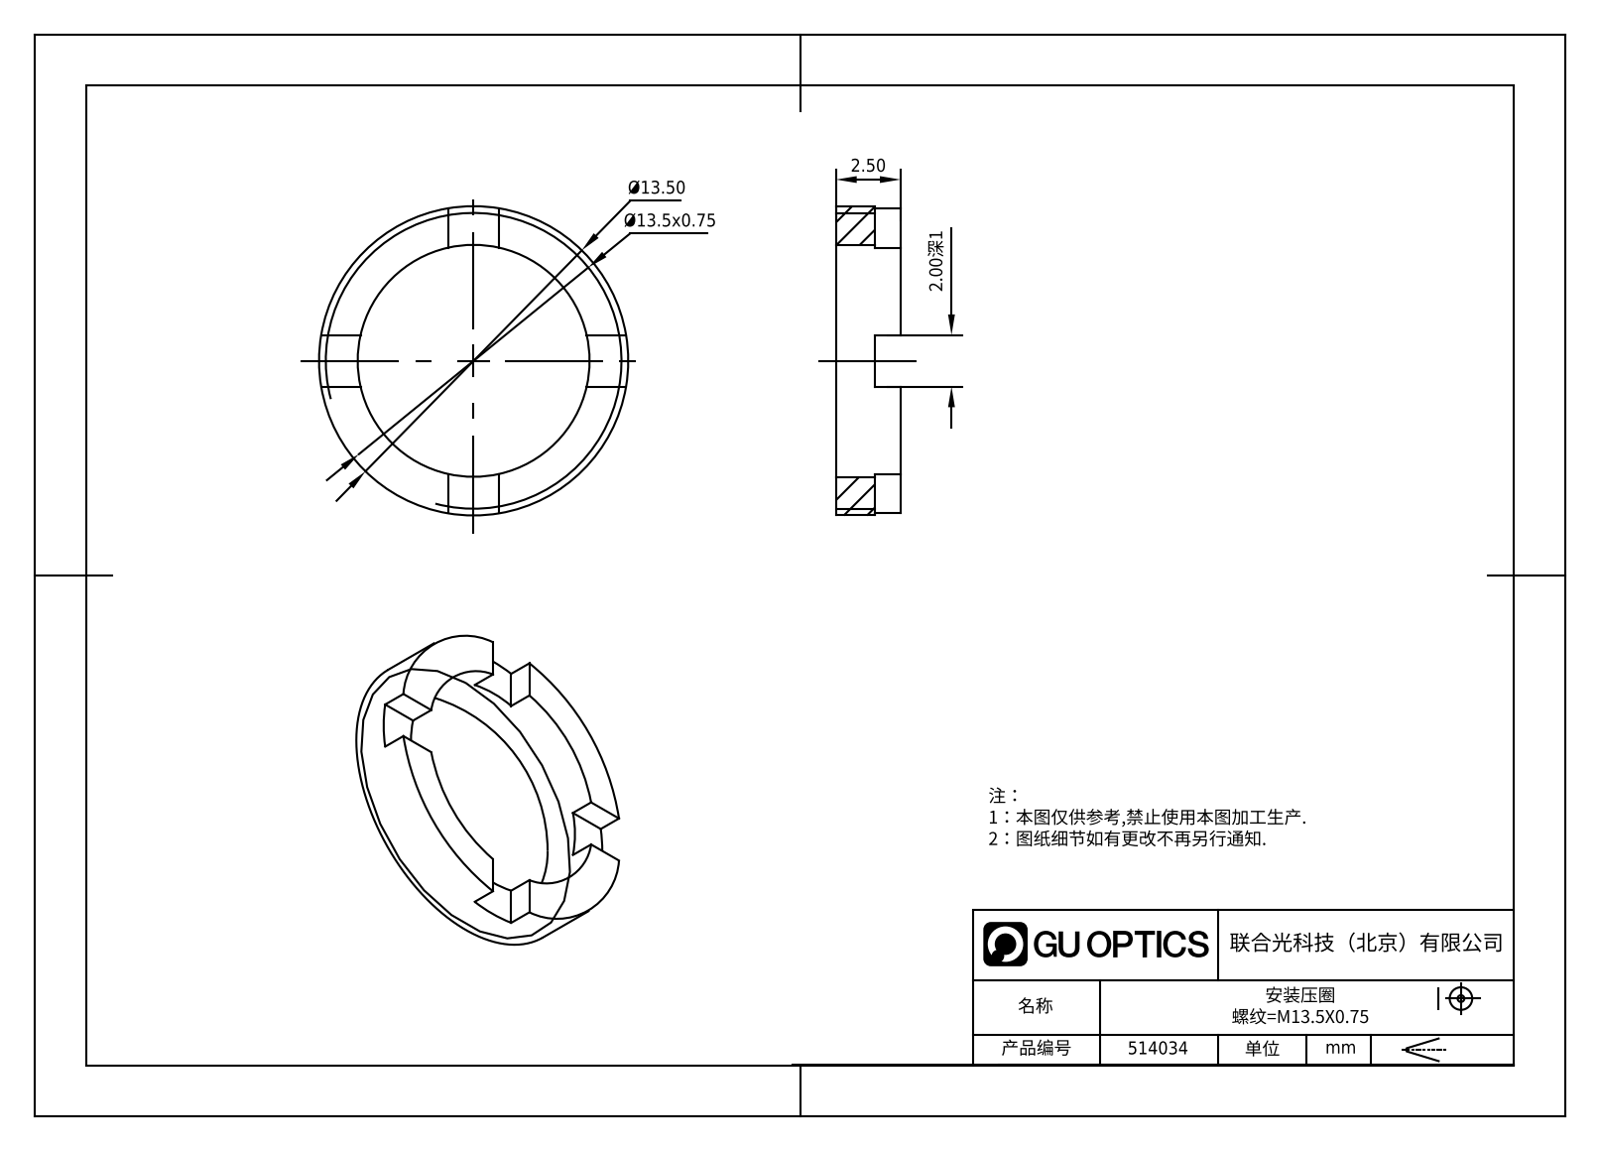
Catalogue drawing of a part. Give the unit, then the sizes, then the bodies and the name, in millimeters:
Units: millimetres
Overall size (bounding box): 13.5 × 13.5 × 2.5
Round holes (diameter × count): ⌀10.5 ×1
Round bosses / shafts (diameter × count): ⌀13.5 ×1
Main face-to-face distances: 2.5, 1.5, 1, 2
Volume: 129 mm³ · Surface area: 298 mm²
Bodies: 1 solid, 21 faces (17 planar, 4 cylindrical, 0 other)
Part name (STEP PRODUCT): 514034
STEP written by: SolidWorks 2020 (CONFIG_CONTROL_DESIGN)
